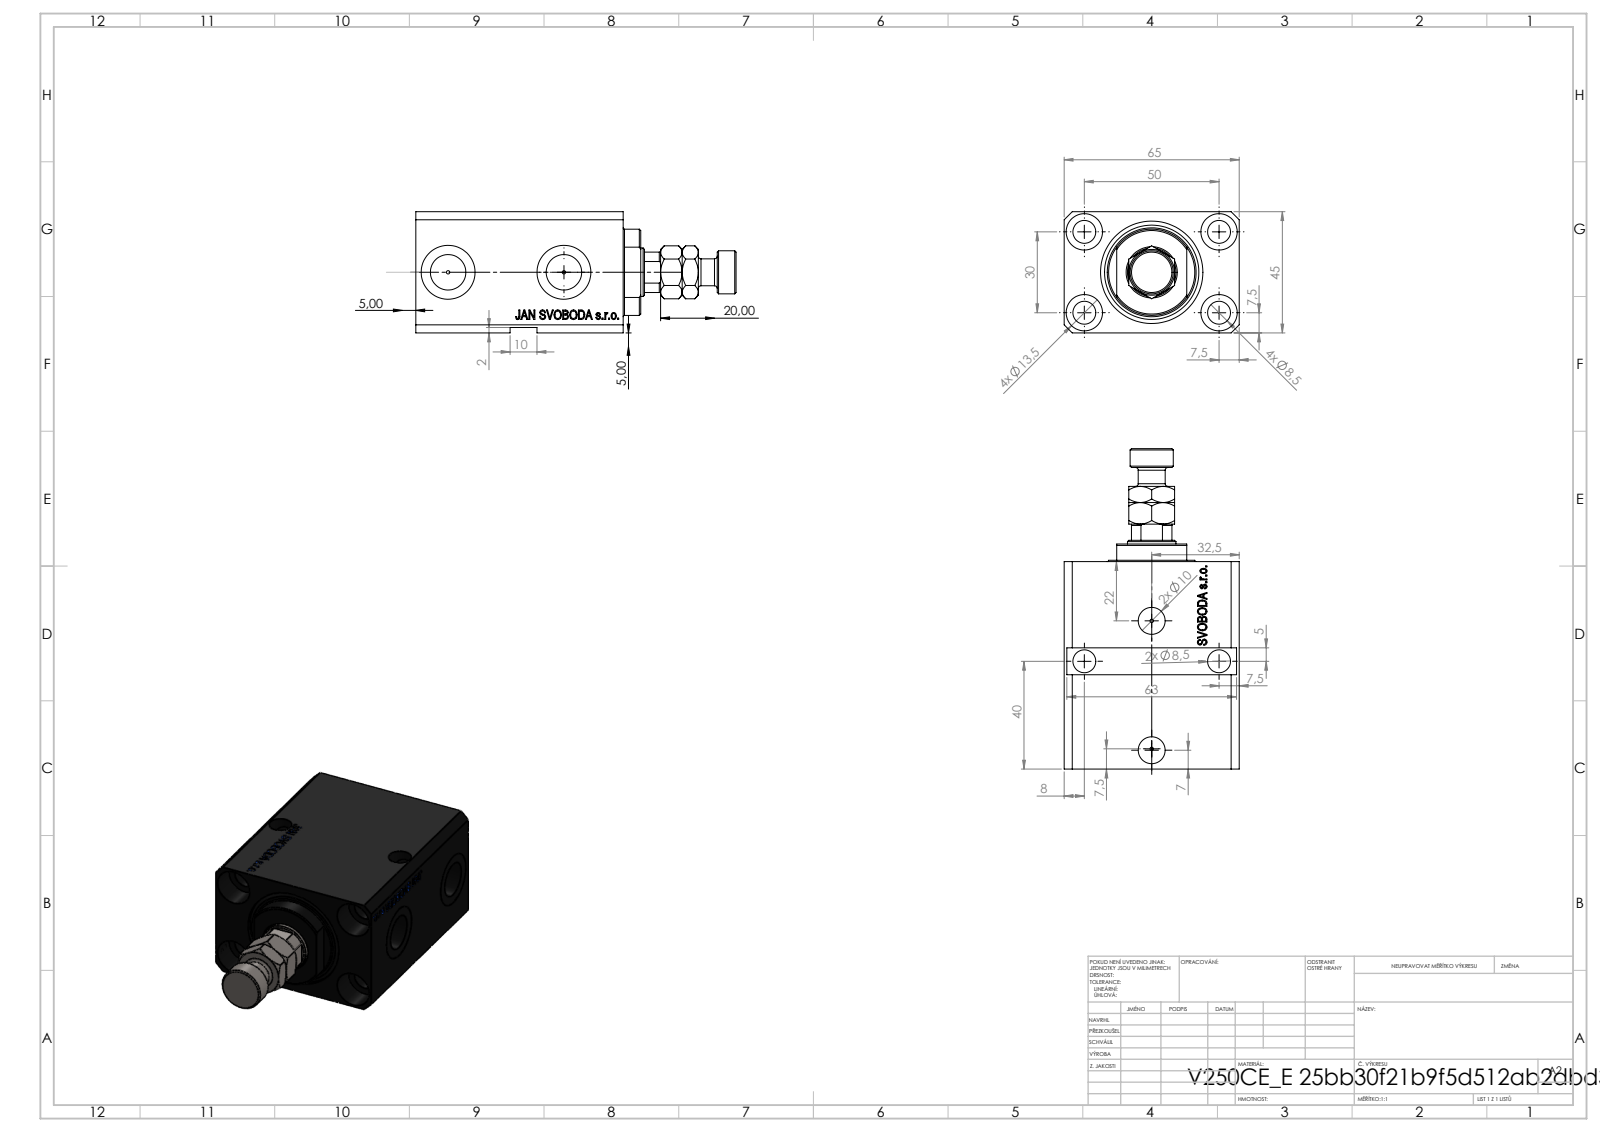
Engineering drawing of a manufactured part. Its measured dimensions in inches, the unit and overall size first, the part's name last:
Units: inches
Overall size (bounding box): 4.685 × 2.559 × 1.772
Round holes (diameter × count): ⌀0.335 ×7, ⌀0.049 ×4, ⌀0.531 ×4, ⌀0.394 ×2, ⌀0.518 ×2, ⌀0.787 ×2, ⌀0.709 ×1, ⌀0.984 ×1, ⌀1.496 ×1
Round bosses / shafts (diameter × count): ⌀0.63 ×1, ⌀0.394 ×1
Partial cylindrical surfaces — rounded edges, fillets, slot ends (radius × count): R0.335 ×1, R0.63 ×1
Main face-to-face distances: 1.772, 2.559, 0.551, 2.48, 3.031, 0.272, 2.209, 2.76, 1.102, 1.693
Hole centre spacings: 1.148, 1.969, 1.181, 1.613, 1.63, 2.296, 0.021, 1.693
Volume: 11.81 in³ · Surface area: 85.96 in²
Bodies: 4 solids, 965 faces (455 planar, 100 cylindrical, 410 other)
Part name (STEP PRODUCT): V250CE_VC_E; V250CE_C_VCP; MFA; V250CE_E_Body
STEP written by: SolidWorks 2019 (CONFIG_CONTROL_DESIGN)
